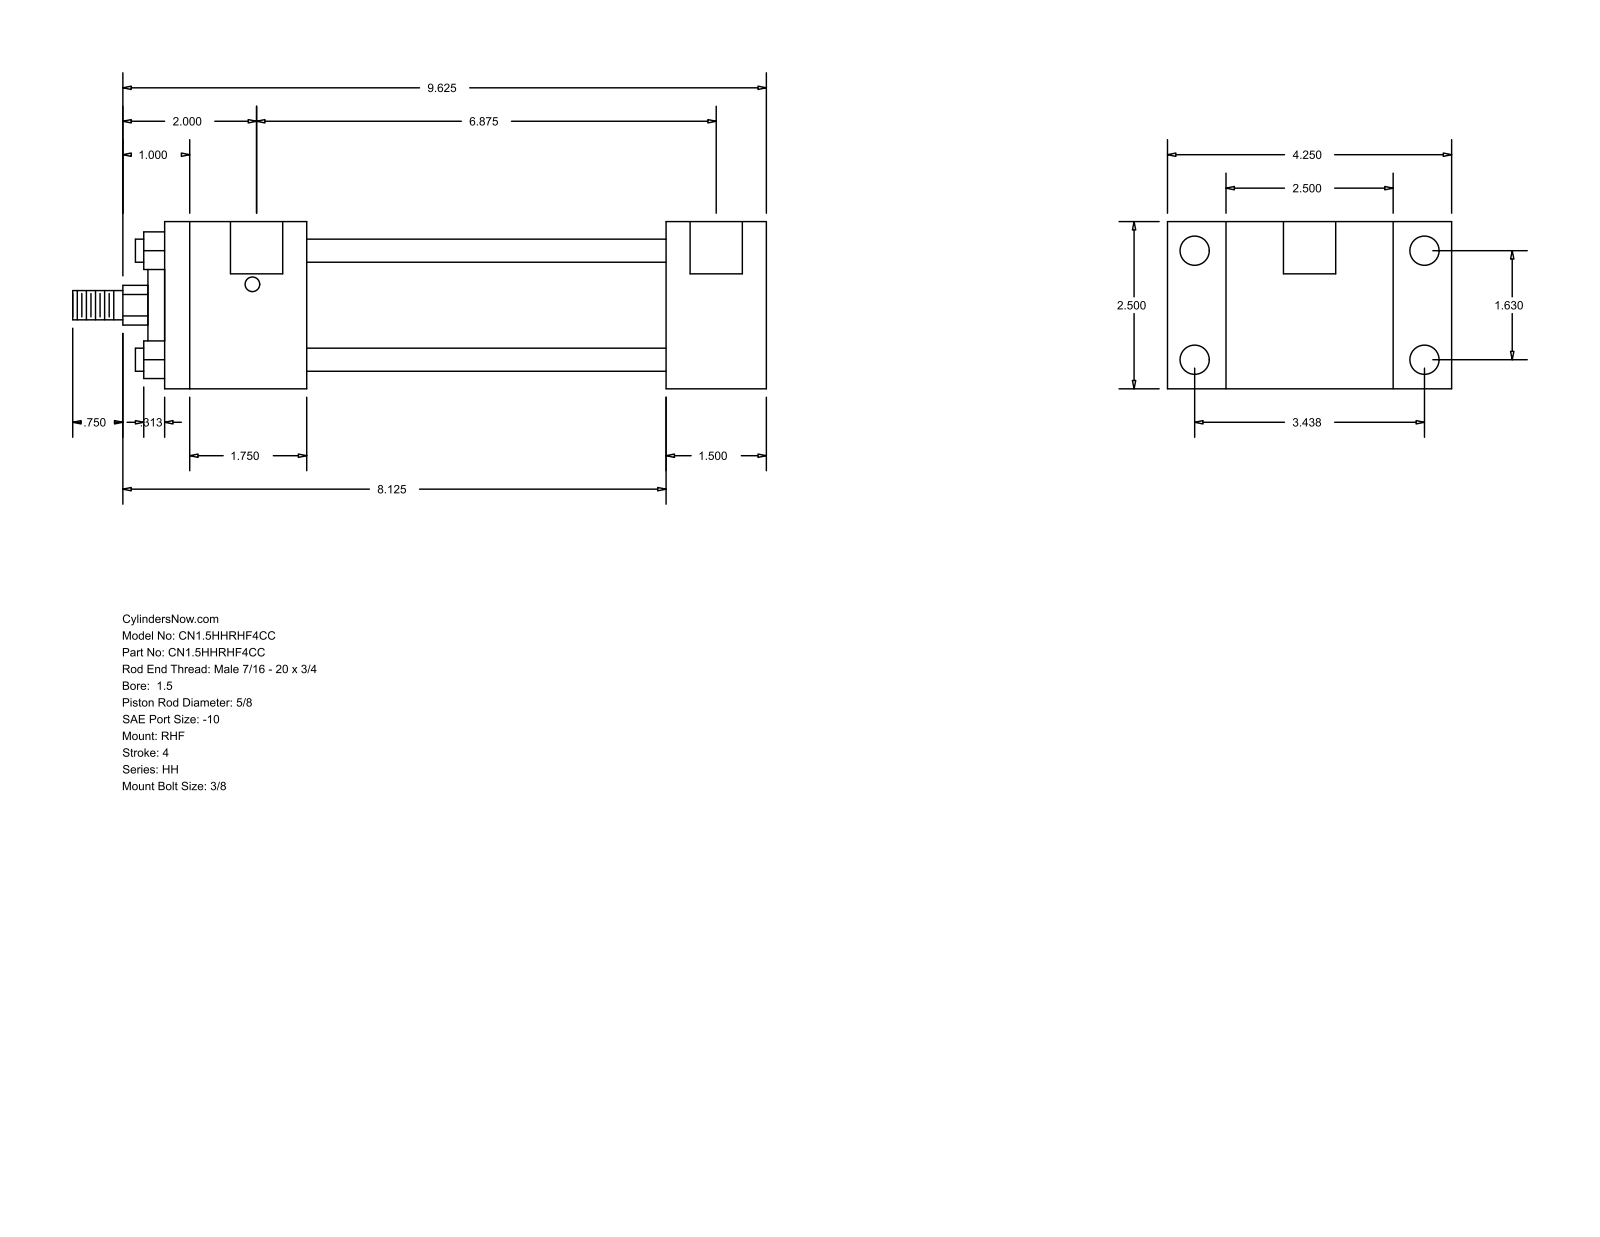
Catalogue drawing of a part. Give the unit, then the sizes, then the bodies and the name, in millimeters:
Units: millimetres
Overall size (bounding box): 263.52 × 107.95 × 63.5
Round holes (diameter × count): ⌀5.56 ×4, ⌀11.13 ×4, ⌀19.84 ×2
Round bosses / shafts (diameter × count): ⌀8.76 ×4, ⌀44.45 ×1, ⌀28.57 ×1, ⌀15.88 ×1, ⌀11.11 ×1
Partial cylindrical surfaces — rounded edges, fillets, slot ends (radius × count): R7.54 ×1
Main face-to-face distances: 63.5, 22.23, 85.73, 38.09, 190.5, 228.59, 107.96, 53.97, 136.53, 174.62
Hole centre spacings: 41.4, 87.32, 96.64, 177.8, 1.58, 1.59, 174.63, 176.21
Bodies: 0 solids, 88 faces (60 planar, 28 cylindrical, 0 other)
Part name (STEP PRODUCT): HH_RHF__0150_0.625
STEP written by: GSSL Pune (CONFIG_CONTROL_DESIGN)
